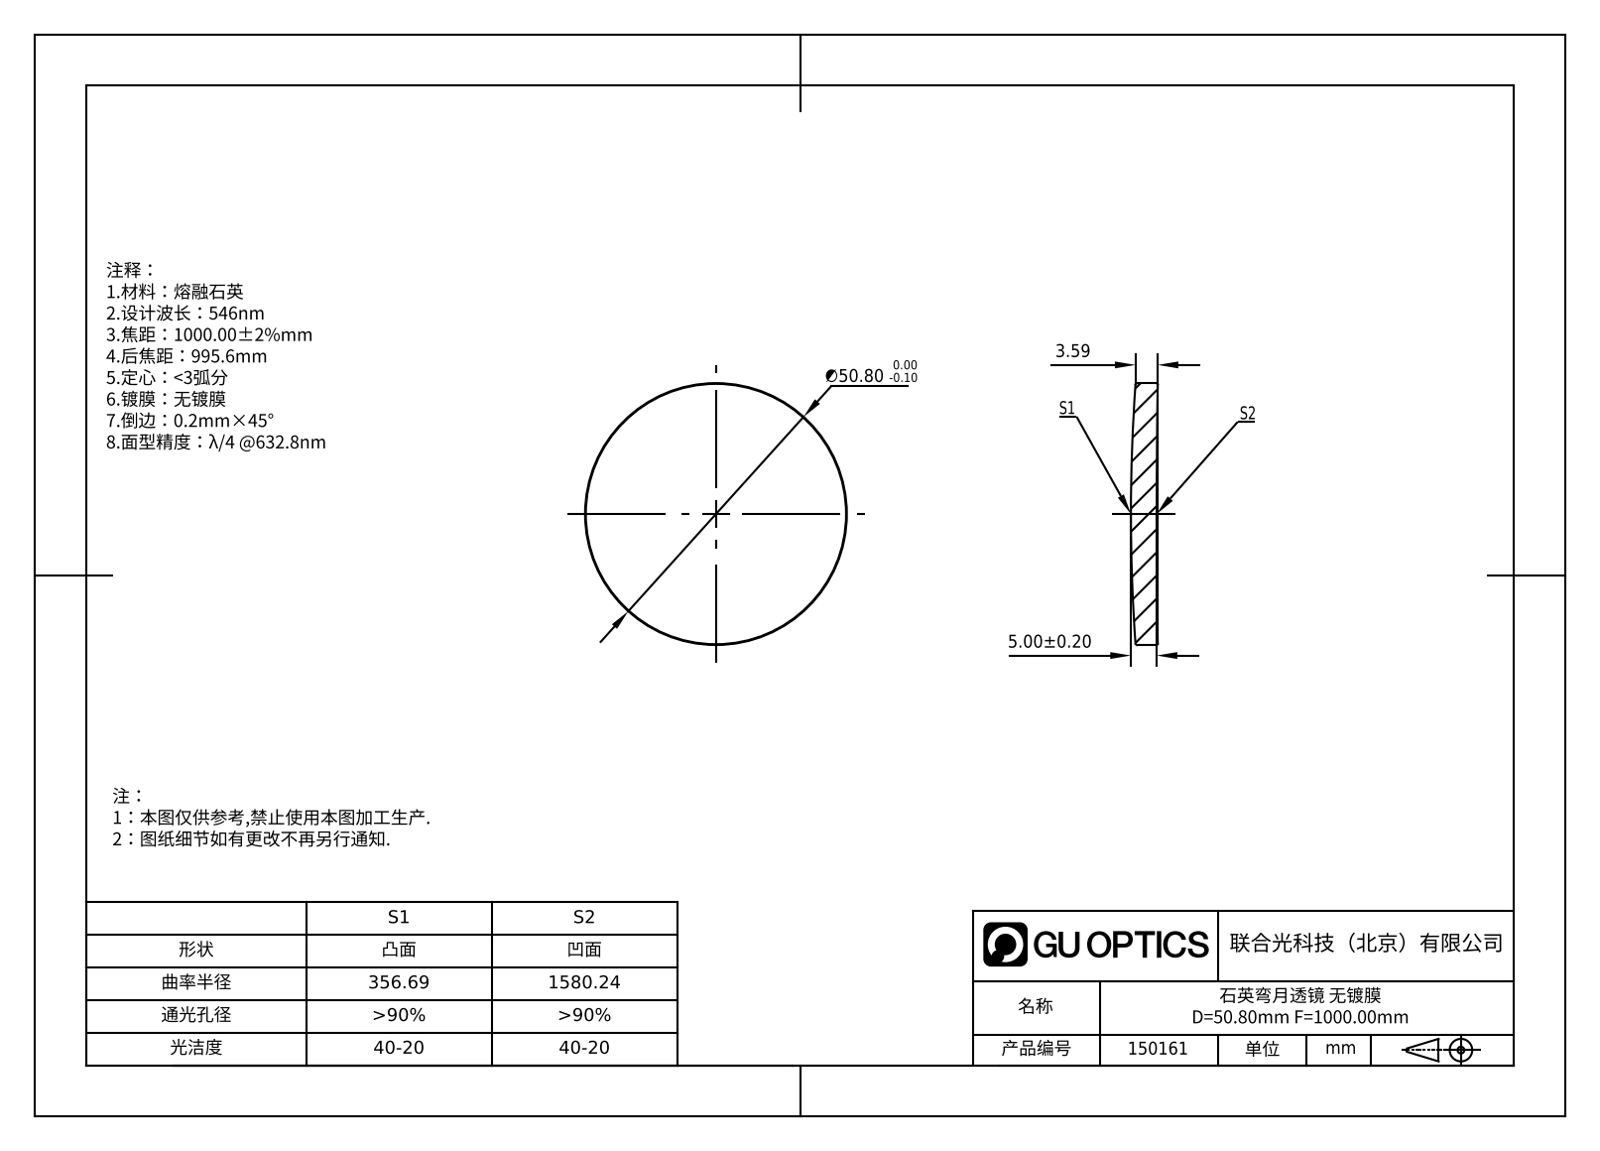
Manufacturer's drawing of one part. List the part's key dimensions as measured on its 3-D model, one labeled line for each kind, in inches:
Part name (STEP PRODUCT): GLM2-050B-1000
STEP written by: SolidWorks 2022 (AUTOMOTIVE_DESIGN)
Units: inches
Bodies: 1 solid, 10 faces (0 planar, 2 cylindrical, 8 other)
Overall size (bounding box): 2 × 2 × 0.205
Volume: 0.575 in³ · Surface area: 7.294 in²
Round bosses / shafts (diameter × count): ⌀2 ×1
